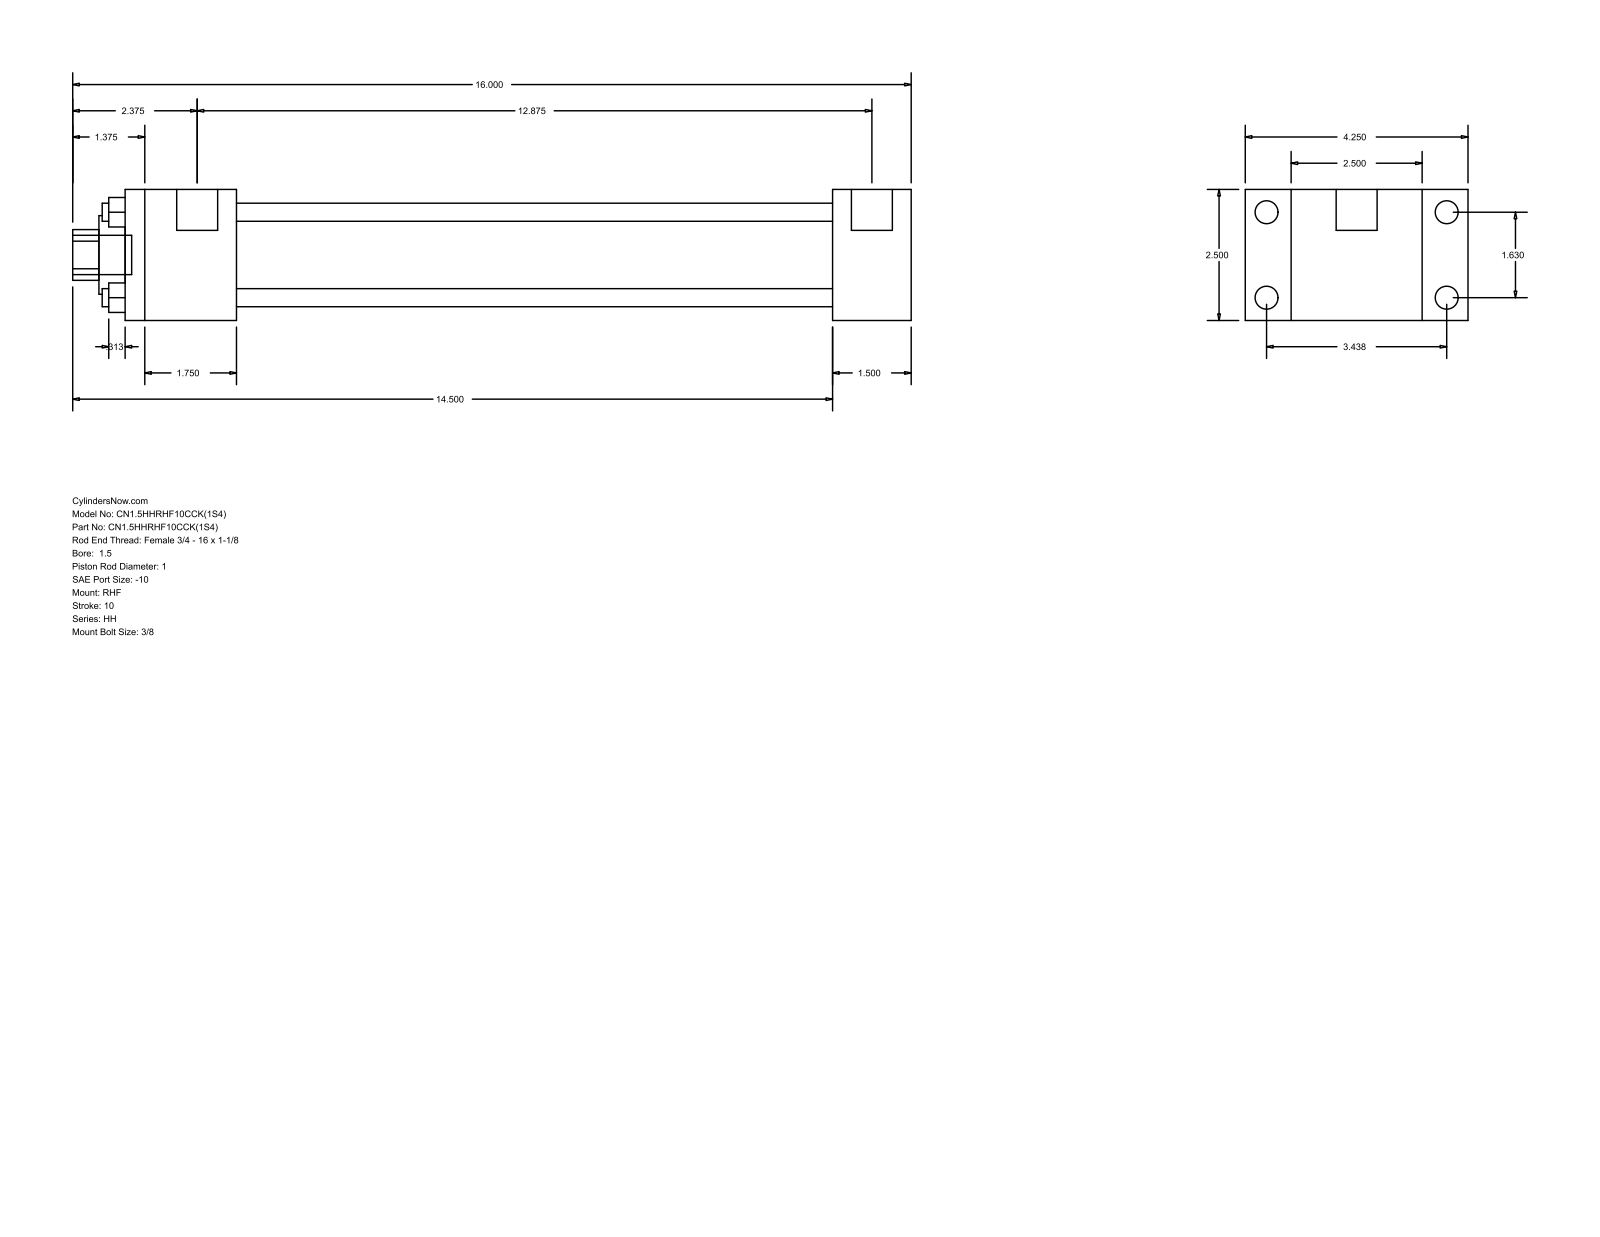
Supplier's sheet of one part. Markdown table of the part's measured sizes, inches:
| quantity | value |
| --- | --- |
| part name | HH_RHF__0150_1 |
| STEP written by | GSSL Pune (CONFIG_CONTROL_DESIGN) |
| units | inches |
| bodies | 0 solids, 88 faces (60 planar, 28 cylindrical, 0 other) |
| overall size | 16 × 4.25 × 2.5 |
| round holes (diameter × count) | 0.345 × 4, 1 × 1, 1.5 × 1, 1.75 × 1 |
| round bosses / shafts (diameter × count) | 0.438 × 4, 0.219 × 4, 0.781 × 2, 0.75 × 1 |
| partial cylindrical surfaces (radius × count) | 0.484 × 1 |
| main face-to-face distances | 2.5, 0.875, 3.375, 1.5, 4.25, 11.375, 12.875, 2.125, 13.5, 15 |
| hole center spacings | 1.152, 1.63, 2.305 |
